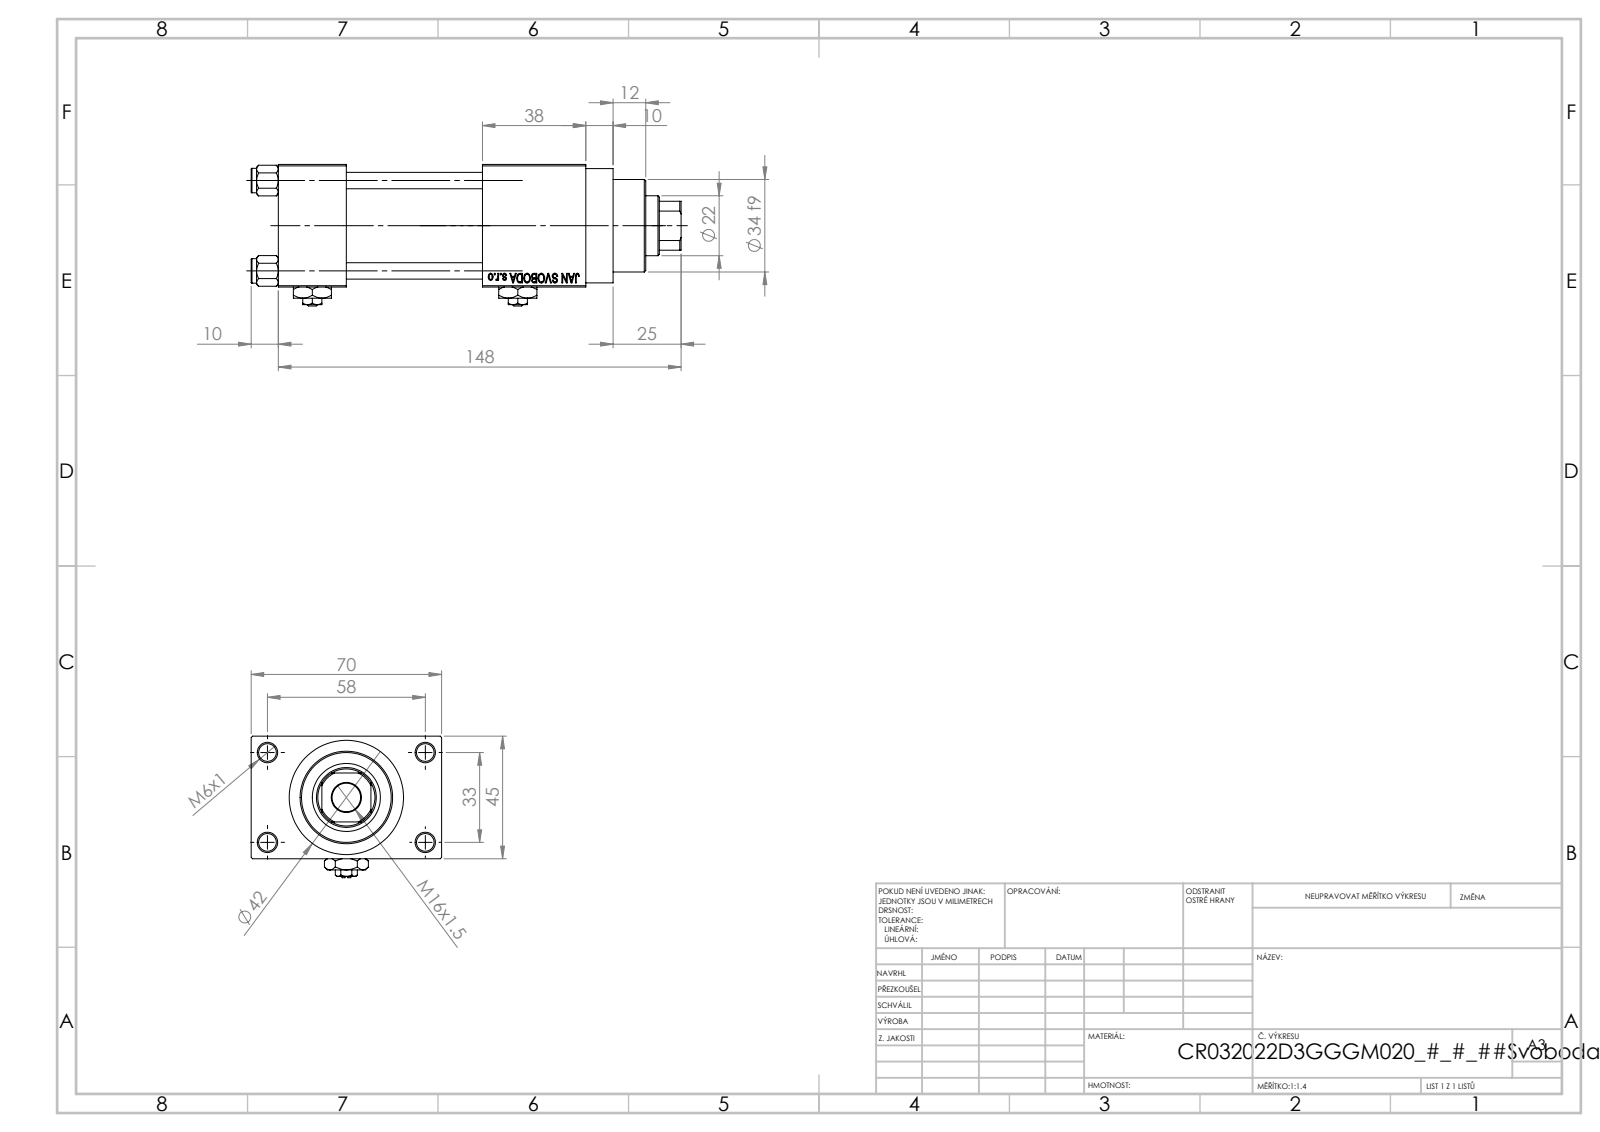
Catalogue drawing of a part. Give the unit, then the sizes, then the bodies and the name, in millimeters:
Units: millimetres
Overall size (bounding box): 158 × 70 × 52
Round holes (diameter × count): ⌀6 ×4, ⌀6.5 ×4, ⌀7 ×2, ⌀13.16 ×2, ⌀20 ×2, ⌀10.5 ×1, ⌀22 ×1, ⌀24 ×1, ⌀25 ×1, ⌀32 ×1, ⌀33 ×1
Round bosses / shafts (diameter × count): ⌀9 ×4, ⌀42 ×1, ⌀38 ×1, ⌀34 ×1
Partial cylindrical surfaces — rounded edges, fillets, slot ends (radius × count): R10.5 ×1
Main face-to-face distances: 45, 25, 12.5, 57.5, 50, 75, 88, 70, 38, 113
Hole centre spacings: 12.4, 23.48, 33.2, 33.37, 35.35, 45.6, 56.35, 33
Volume: 243 368 mm³ · Surface area: 81 200 mm²
Bodies: 13 solids, 1202 faces (542 planar, 100 cylindrical, 560 other)
Part name (STEP PRODUCT): V215CR_D_TYCINKA; V215_VC_A; Zatka_pro_OIL_PORT; V215CR_D_Body (+2 more)
STEP written by: SolidWorks 2019 (CONFIG_CONTROL_DESIGN)
